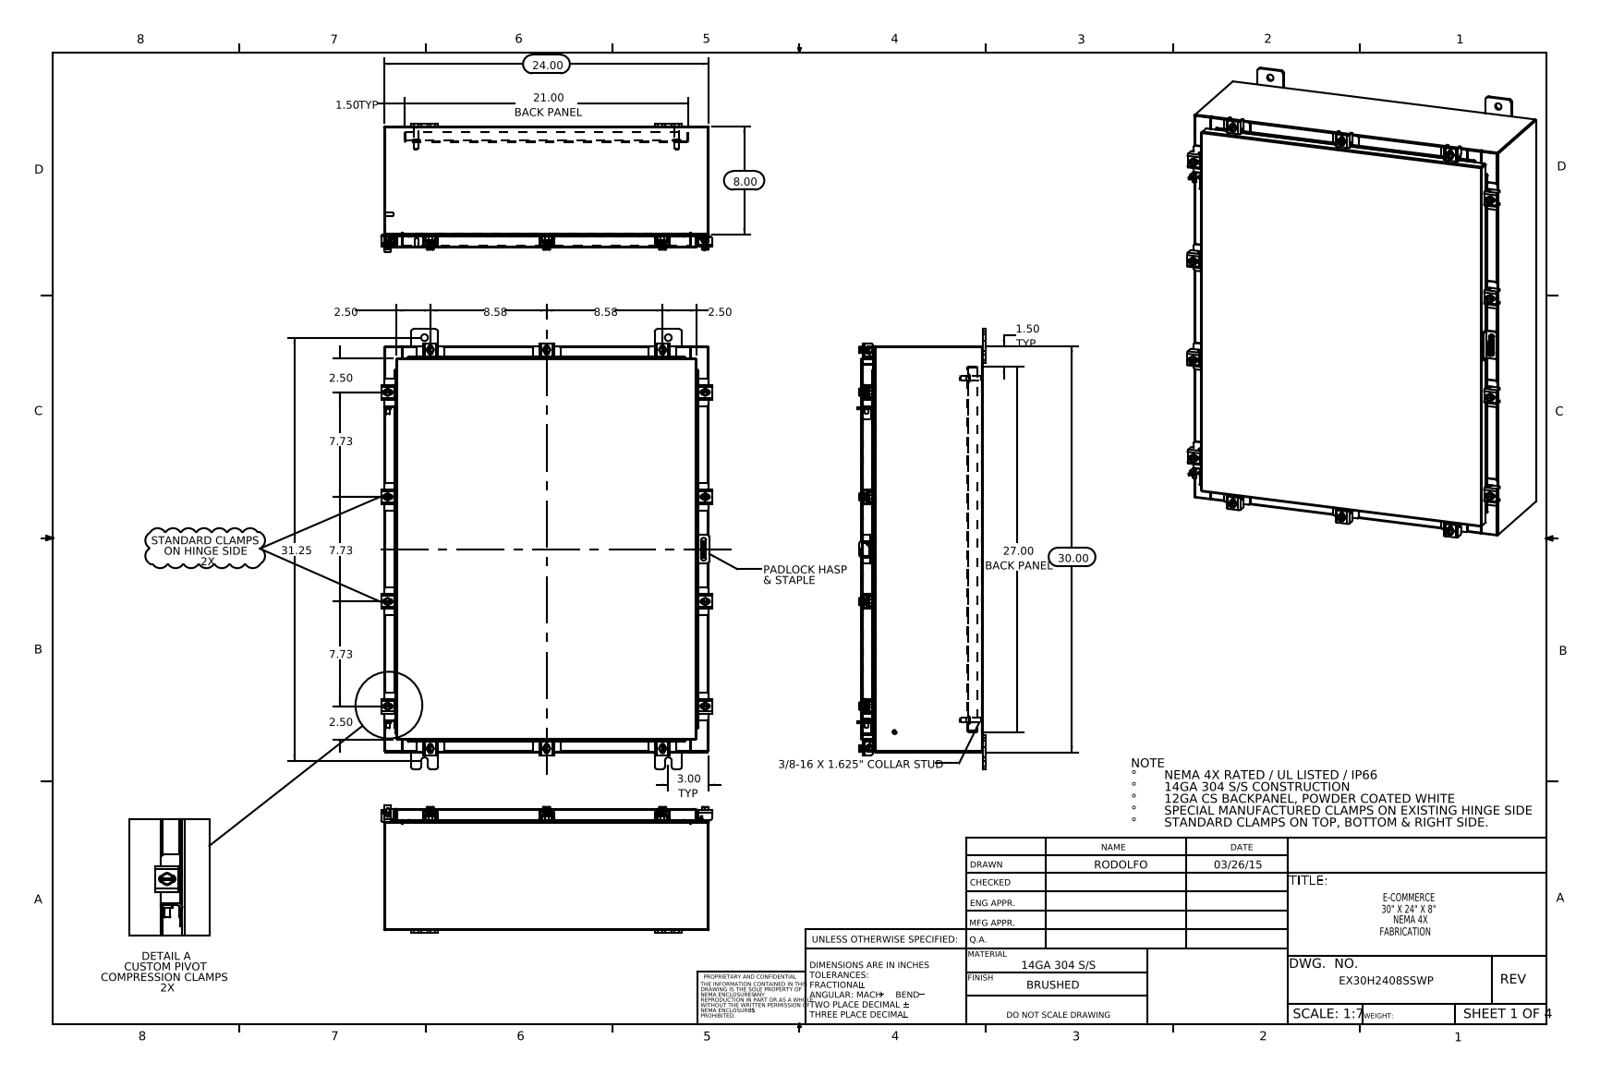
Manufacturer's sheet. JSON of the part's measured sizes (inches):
{"part_name": "EX30H2408SSWP Standard Clamps; EX30H2408SSWP Clamp Bracket; ATEX CLAMP HINGE BRAKET; HW-CLN-NH-20330 (+8 more)", "step_written_by": "SolidWorks 2014 (CONFIG_CONTROL_DESIGN)", "units": "inches", "bodies": {"solids": 91, "faces": 2272, "planar": 1211, "cylindrical": 885, "other": 176}, "overall_size": [32.5, 24.421, 9.453], "volume_in3": 264.6, "surface_area_in2": 6573, "round_holes": [[0.213, 14], [0.26, 14], [0.5, 8], [0.125, 1], [0.25, 1]], "round_bosses_or_shafts": [[0.5, 14], [0.25, 14], [0.399, 12], [0.625, 4], [0.375, 4], [0.33, 4], [0.315, 2], [0.236, 2]], "partial_cylinders_radius": [[0.06, 62], [0.141, 28], [0.013, 26], [0.12, 26], [0.19, 24], [0.088, 22], [0.09, 20], [0.05, 19]], "face_to_face_distances": [0.075, 8.9, 8.975, 8.826, 0.104, 1, 1.075, 7.826, 7.9, 1.179], "hole_center_spacings": [2.347, 4.44, 20.544, 23.451, 24.31, 26.507, 27.37, 32.286]}
